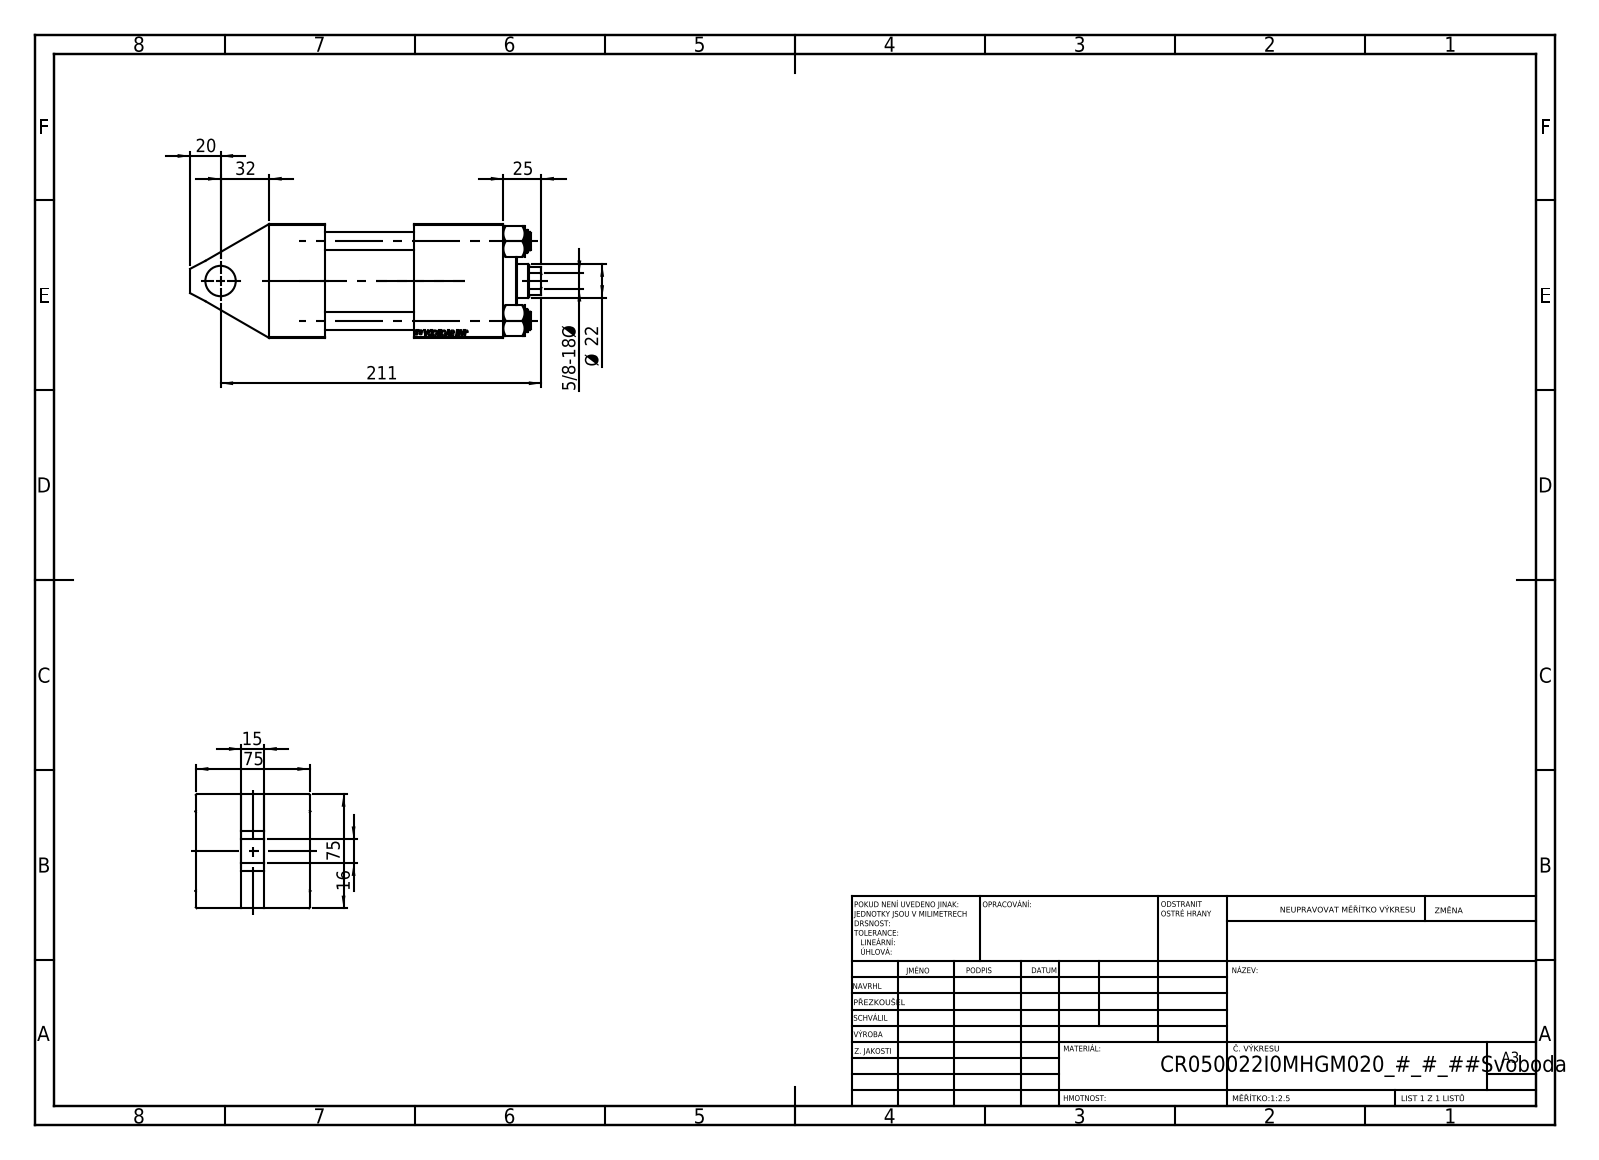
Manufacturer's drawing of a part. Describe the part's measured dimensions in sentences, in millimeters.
The part is named "NUT_M5_I; V215CR_I_Body; V215_VC_A; V215CR_VCP_I (+1 more)". Its 3-D file was written by "SolidWorks 2019 (CONFIG_CONTROL_DESIGN)". It is 11 solids with 1079 faces: 502 planar, 81 cylindrical and 496 other. Overall it measures 231 by 75.54 by 75 millimeters. Its volume is 699 574 cubic millimeters and its surface area 156 292 square millimeters. Round holes: 4 of diameter 12, 2 of diameter 7, 2 of diameter 20.96, 2 of diameter 30, 1 of diameter 10.5, 1 of diameter 20, 1 of diameter 22, 1 of diameter 25, 1 of diameter 41, 1 of diameter 50, 1 of diameter 53. Round bosses or shafts: 4 of diameter 15, 1 of diameter 56, 1 of diameter 34. Partial cylindrical surfaces (rounded edges, fillets, slot ends): 1 of radius 10.5. The main face-to-face distances are 75, 117, 37, 154, 45, 30, 95, 58, 59, 125.3. The hole center spacings are 36.98, 52.3, 73.96, 50.5, 93.5, 144.
